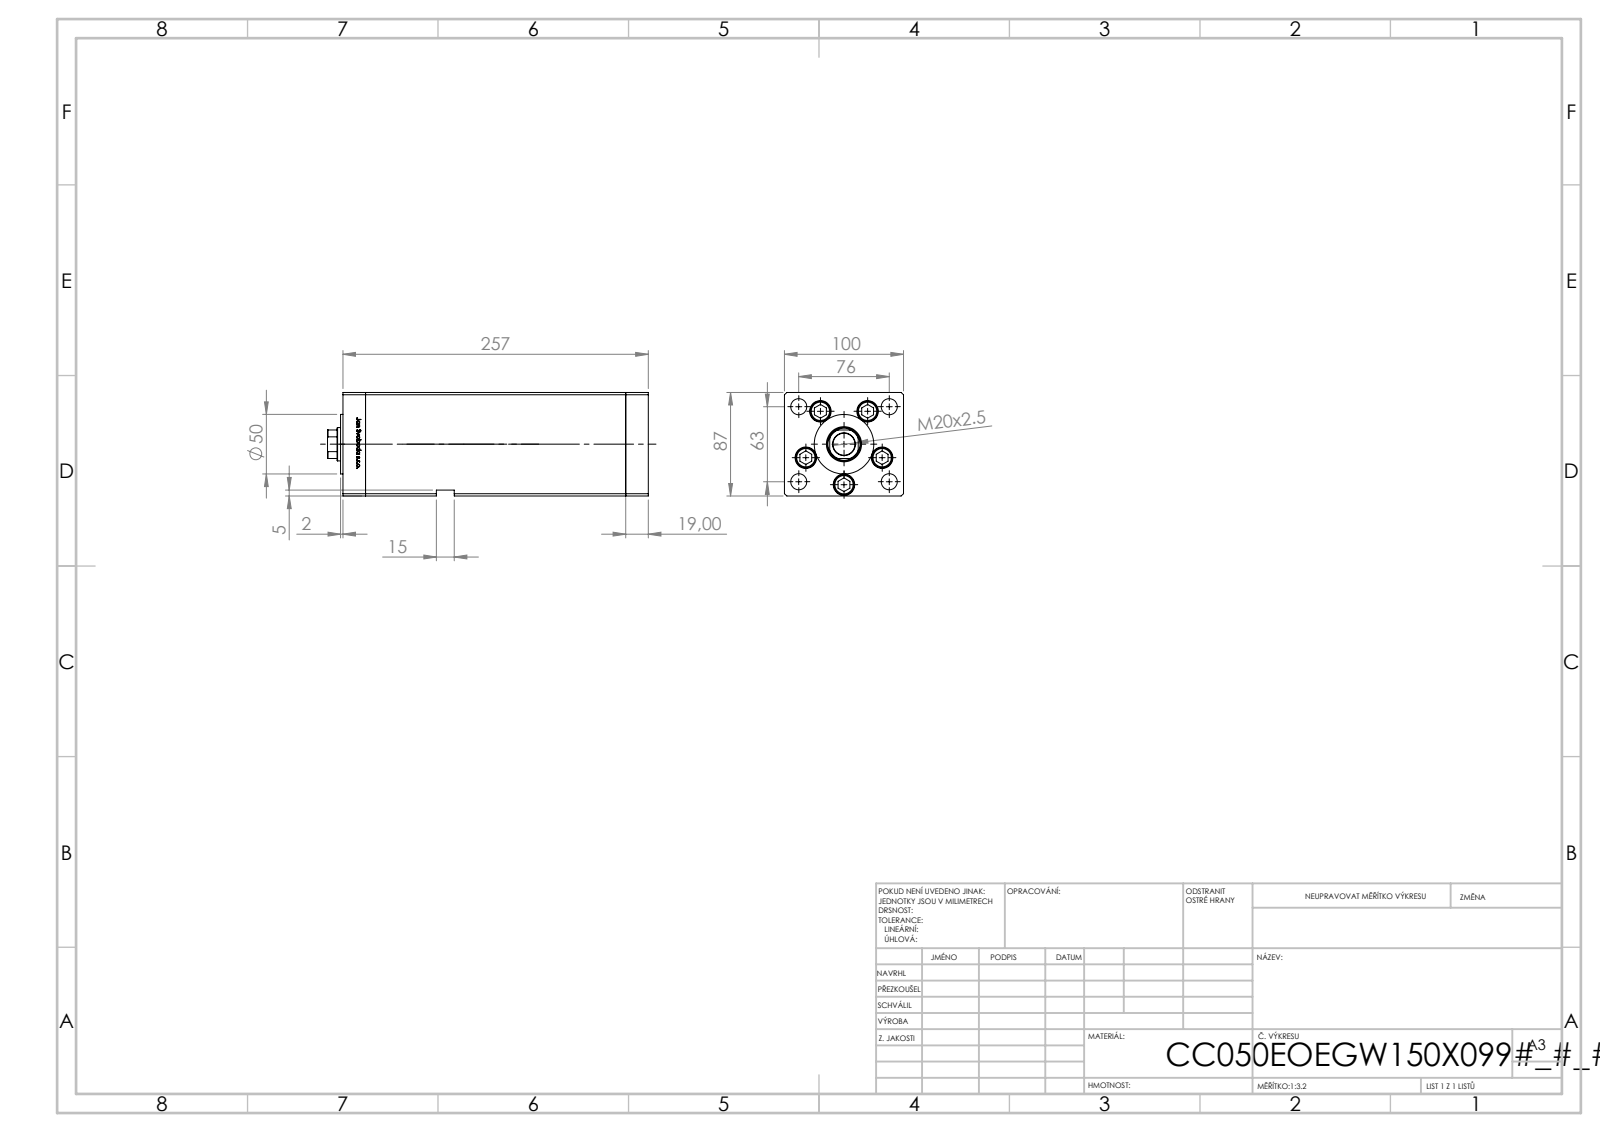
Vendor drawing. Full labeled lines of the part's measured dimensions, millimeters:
Part name (STEP PRODUCT): V220C_FRONT_E; V220C BACK_E; V220C_E MIDDLE; ALLEN BOLT (+1 more)
STEP written by: SolidWorks 2019 (CONFIG_CONTROL_DESIGN)
Units: millimetres
Bodies: 14 solids, 1214 faces (475 planar, 165 cylindrical, 574 other)
Overall size (bounding box): 269.5 × 100 × 87
Volume: 1 865 000 mm³ · Surface area: 265 760 mm²
Round holes (diameter × count): ⌀13.5 ×11, ⌀18 ×5, ⌀18.5 ×5, ⌀12.5 ×4, ⌀2 ×2, ⌀13.16 ×2, ⌀28 ×1, ⌀29.5 ×1
Round bosses / shafts (diameter × count): ⌀17 ×5, ⌀8 ×5, ⌀50 ×1
Partial cylindrical surfaces — rounded edges, fillets, slot ends (radius × count): R0.93 ×2, R13.5 ×1
Main face-to-face distances: 100, 87, 19, 218.5, 237.5, 34.25, 256.5, 15.25, 203.25, 222.25
Hole centre spacings: 34, 18.59, 39.64, 49.36, 57.95, 21.03, 38.08, 39.27
